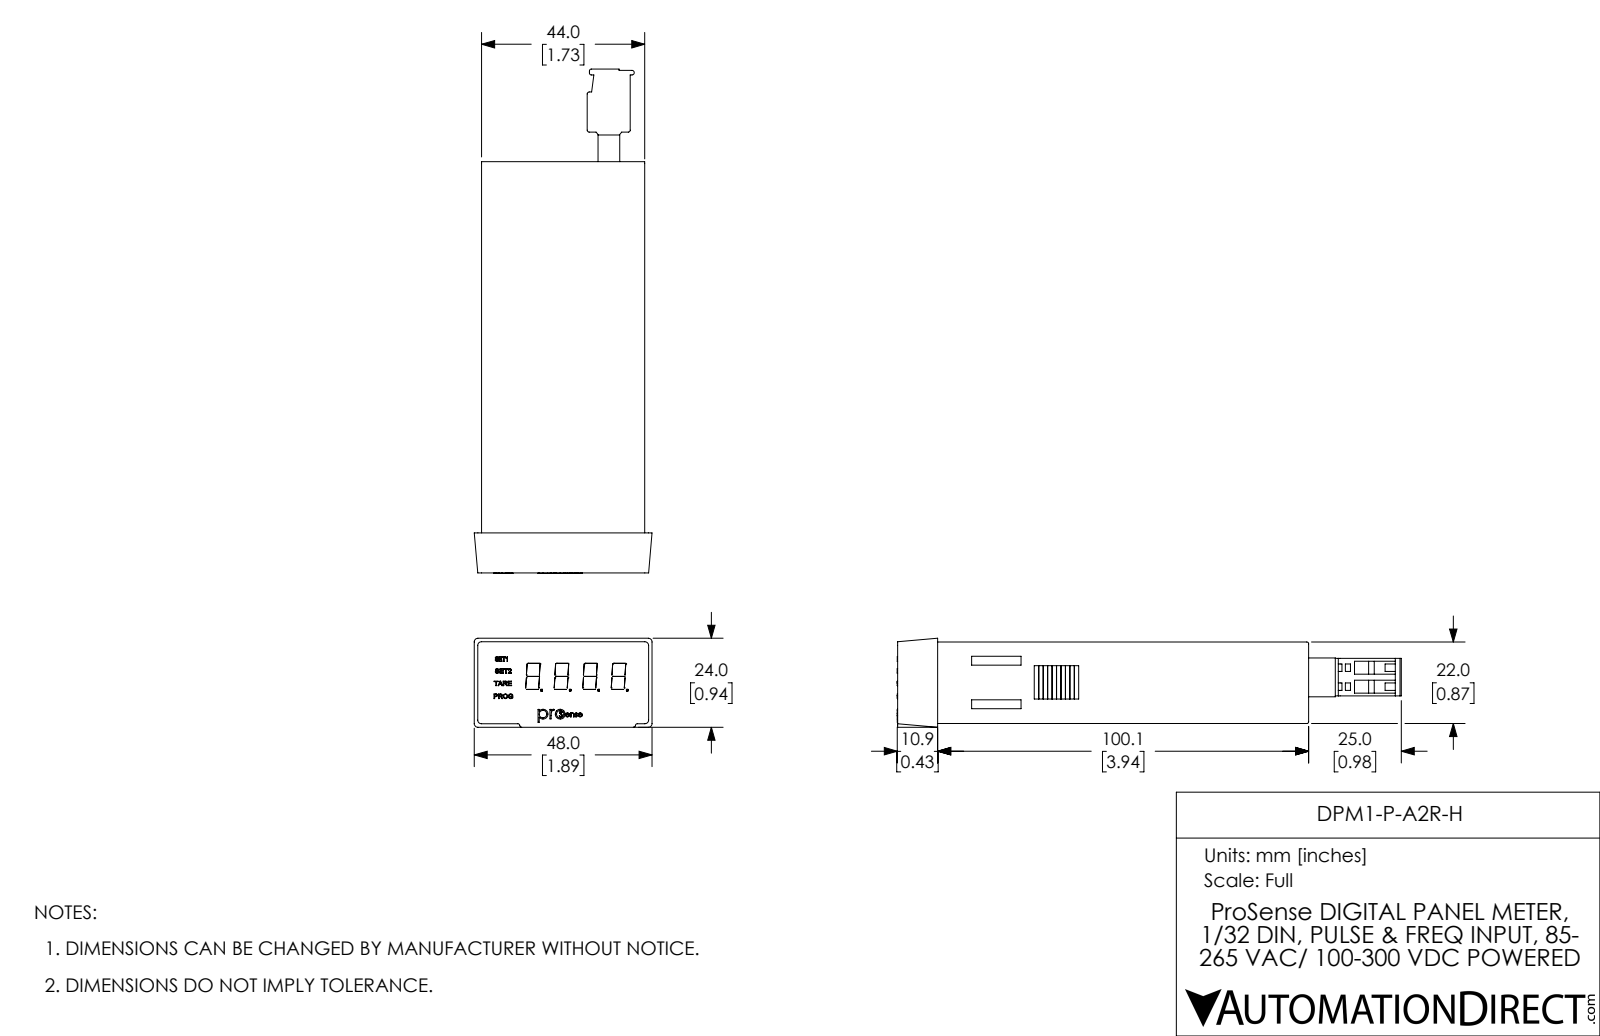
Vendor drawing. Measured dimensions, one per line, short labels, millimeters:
name: DPM1-P-2R Coord fXT
written by: SolidWorks 2017 (AUTOMOTIVE_DESIGN)
unit: mm
bodies: 6 solids, 1467 faces (1124 planar, 167 cylindrical, 176 other)
size: 136 × 48 × 24.9
volume: 42 160 mm³; area: 39 160 mm²
holes: 7× ⌀1, 7× ⌀2, 6× ⌀2, 6× ⌀3, 6× ⌀3.9
rounds: 14× R0.3, 14× R0.4, 14× R0.5, 7× R1.8, 7× R1.8, 6× R3.1, 4× R1, 2× R0.6
face distances: 1.5, 20.5, 22, 19, 42.5, 44, 41, 1.3, 11, 109.6
hole spacings: 13.7, 3.5, 5, 5, 5.1, 5.1, 7, 7.3
